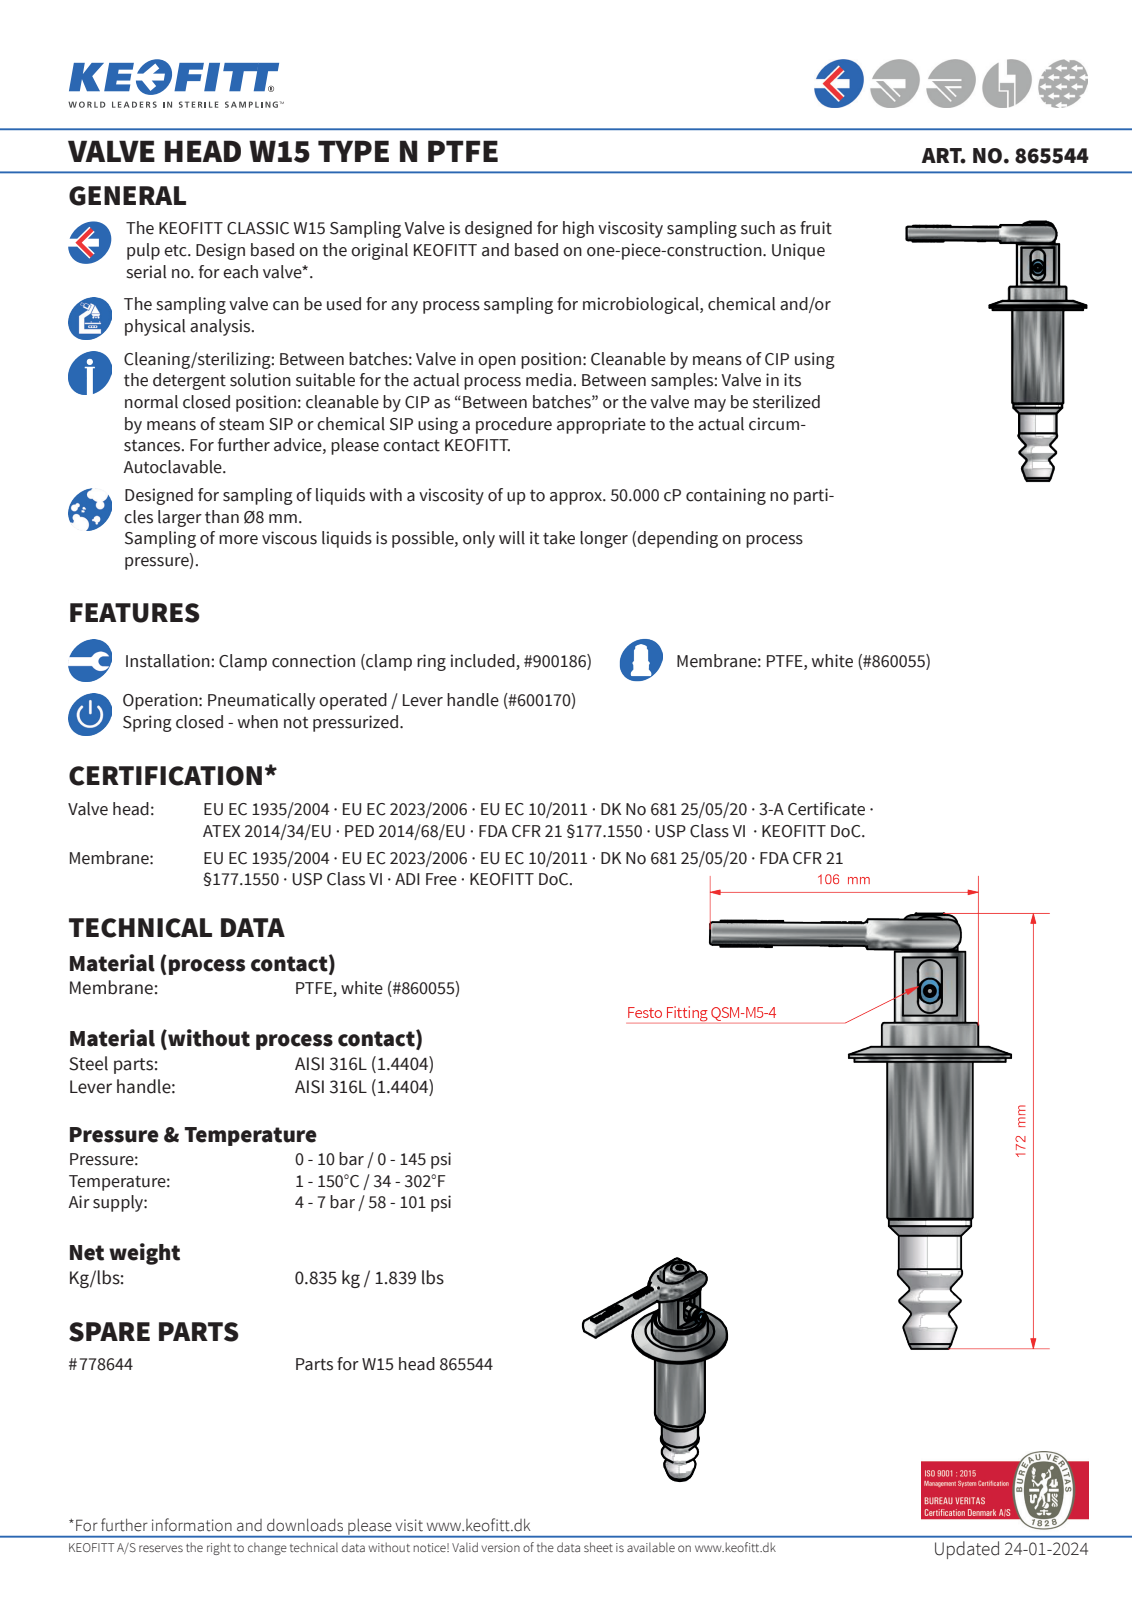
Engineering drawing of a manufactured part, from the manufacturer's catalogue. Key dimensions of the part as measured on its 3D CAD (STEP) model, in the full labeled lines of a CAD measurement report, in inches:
Part name (STEP PRODUCT): 865544
STEP written by: Autodesk Inventor 2022 (AUTOMOTIVE_DESIGN)
Units: inches
Bodies: 16 solids, 990 faces (362 planar, 221 cylindrical, 407 other)
Overall size (bounding box): 6.776 × 5.306 × 4.903
Volume: 11.64 in³ · Surface area: 135.9 in²
Round holes (diameter × count): ⌀0.157 ×2, ⌀0.236 ×2, ⌀0.094 ×1, ⌀0.118 ×1, ⌀0.169 ×1, ⌀0.194 ×1, ⌀0.199 ×1, ⌀0.248 ×1, ⌀0.307 ×1, ⌀0.394 ×1, ⌀0.398 ×1, ⌀0.437 ×1
Round bosses / shafts (diameter × count): ⌀0.315 ×2, ⌀2.701 ×1, ⌀2.346 ×1, ⌀1.496 ×1, ⌀1.339 ×1, ⌀1.327 ×1, ⌀1.28 ×1, ⌀1.276 ×1
Partial cylindrical surfaces — rounded edges, fillets, slot ends (radius × count): R0.039 ×40, R0.079 ×22, R0.02 ×14, R0.02 ×6, R0.157 ×4, R0.016 ×2, R0.059 ×2, R0.154 ×2
Main face-to-face distances: 2.441, 0.278, 0.177, 1.496, 0.36, 1.122, 2.677, 1.339, 1.732, 0.236
Hole centre spacings: 0.867, 2.441, 3.307
